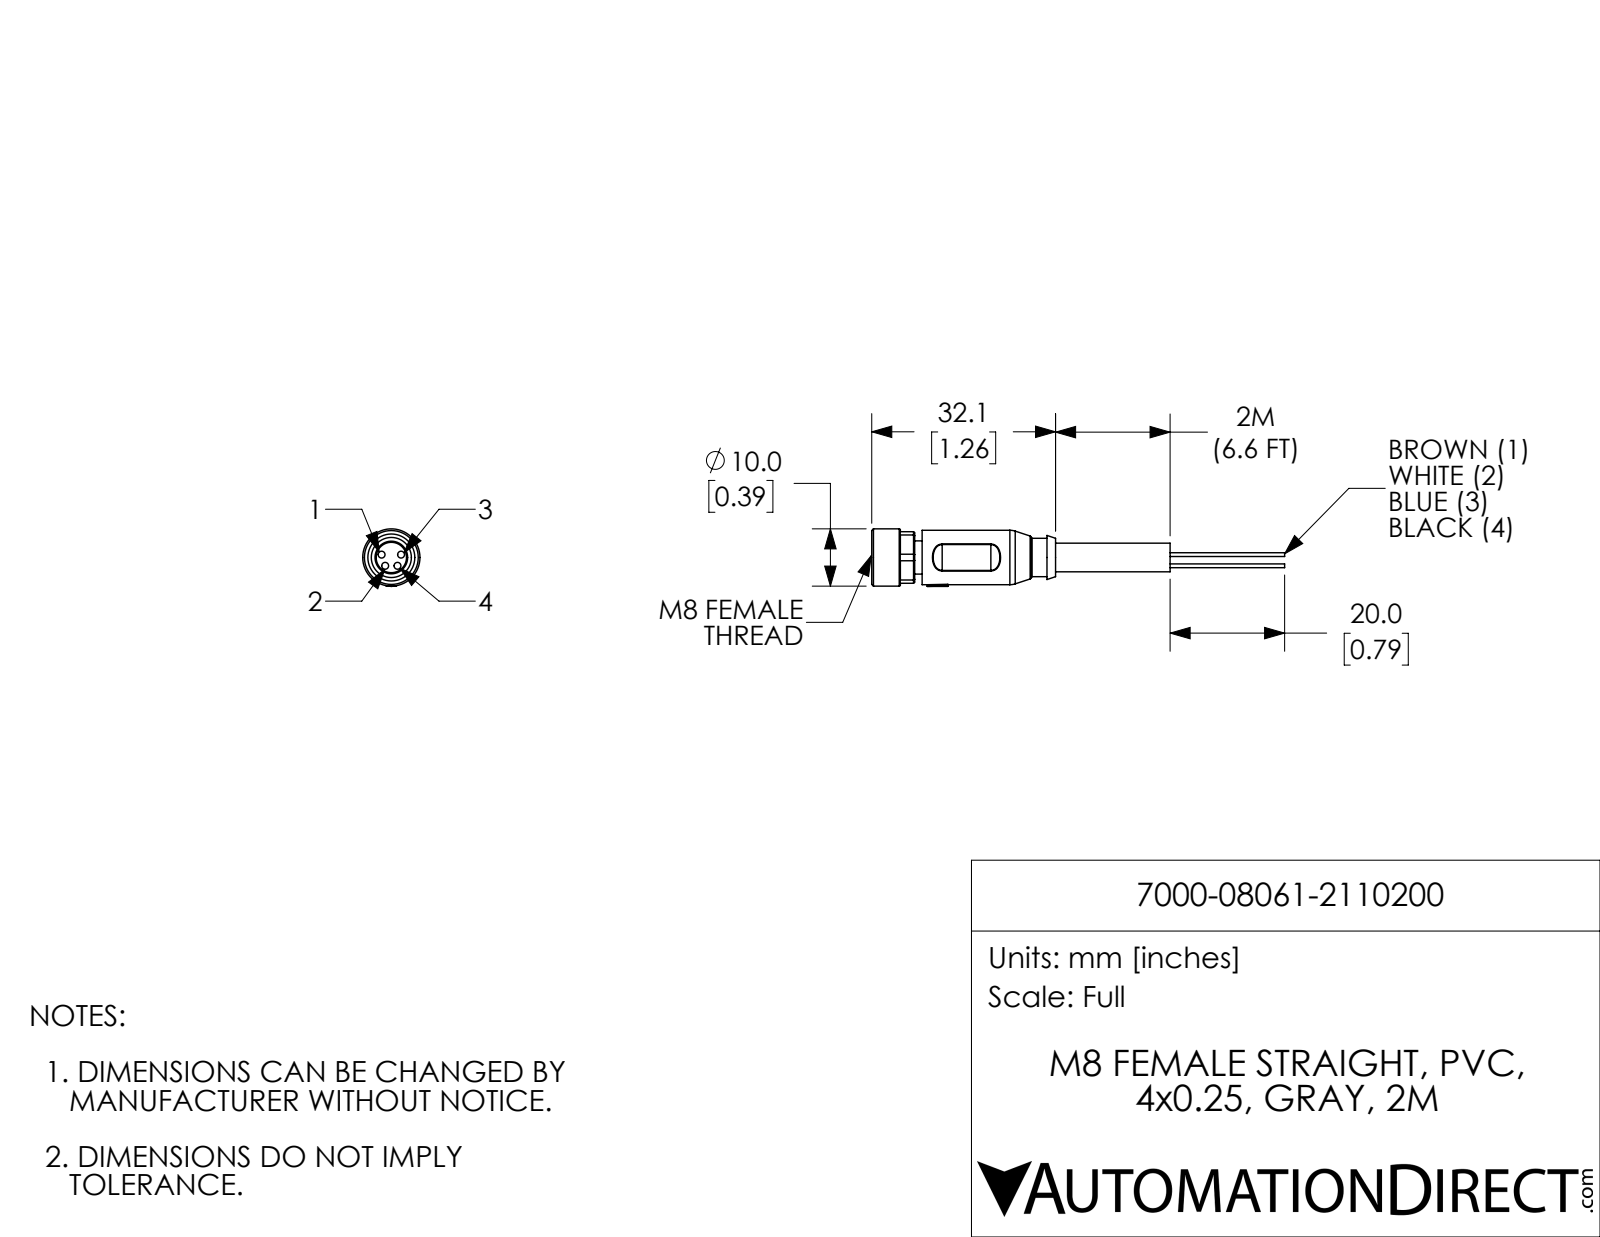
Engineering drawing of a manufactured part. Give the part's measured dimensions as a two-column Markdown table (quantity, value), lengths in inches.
| quantity | value |
| --- | --- |
| part name | 7000-08061-2110200 |
| STEP written by | SolidWorks 2017 (AUTOMOTIVE_DESIGN) |
| units | inches |
| bodies | 1 solid, 115 faces (38 planar, 46 cylindrical, 31 other) |
| overall size | 2.839 × 0.396 × 0.394 |
| volume | 0.141 in³ |
| surface area | 2.944 in² |
| round holes (diameter × count) | 0.047 × 4, 0.276 × 1 |
| round bosses / shafts (diameter × count) | 0.026 × 4, 0.394 × 1, 0.374 × 1, 0.264 × 1, 0.228 × 1, 0.224 × 1, 0.197 × 1 |
| partial cylindrical surfaces (radius × count) | 0.008 × 4, 0.098 × 4, 0.193 × 1, 0.199 × 1 |
| main face-to-face distances | 0.327, 0.051, 0.969, 0.354, 0.059, 0.028, 1.756, 1.705, 0.268, 0.319 |
| hole center spacings | 0.07, 0.071, 0.081, 0.133, 0.084, 0.134 |
